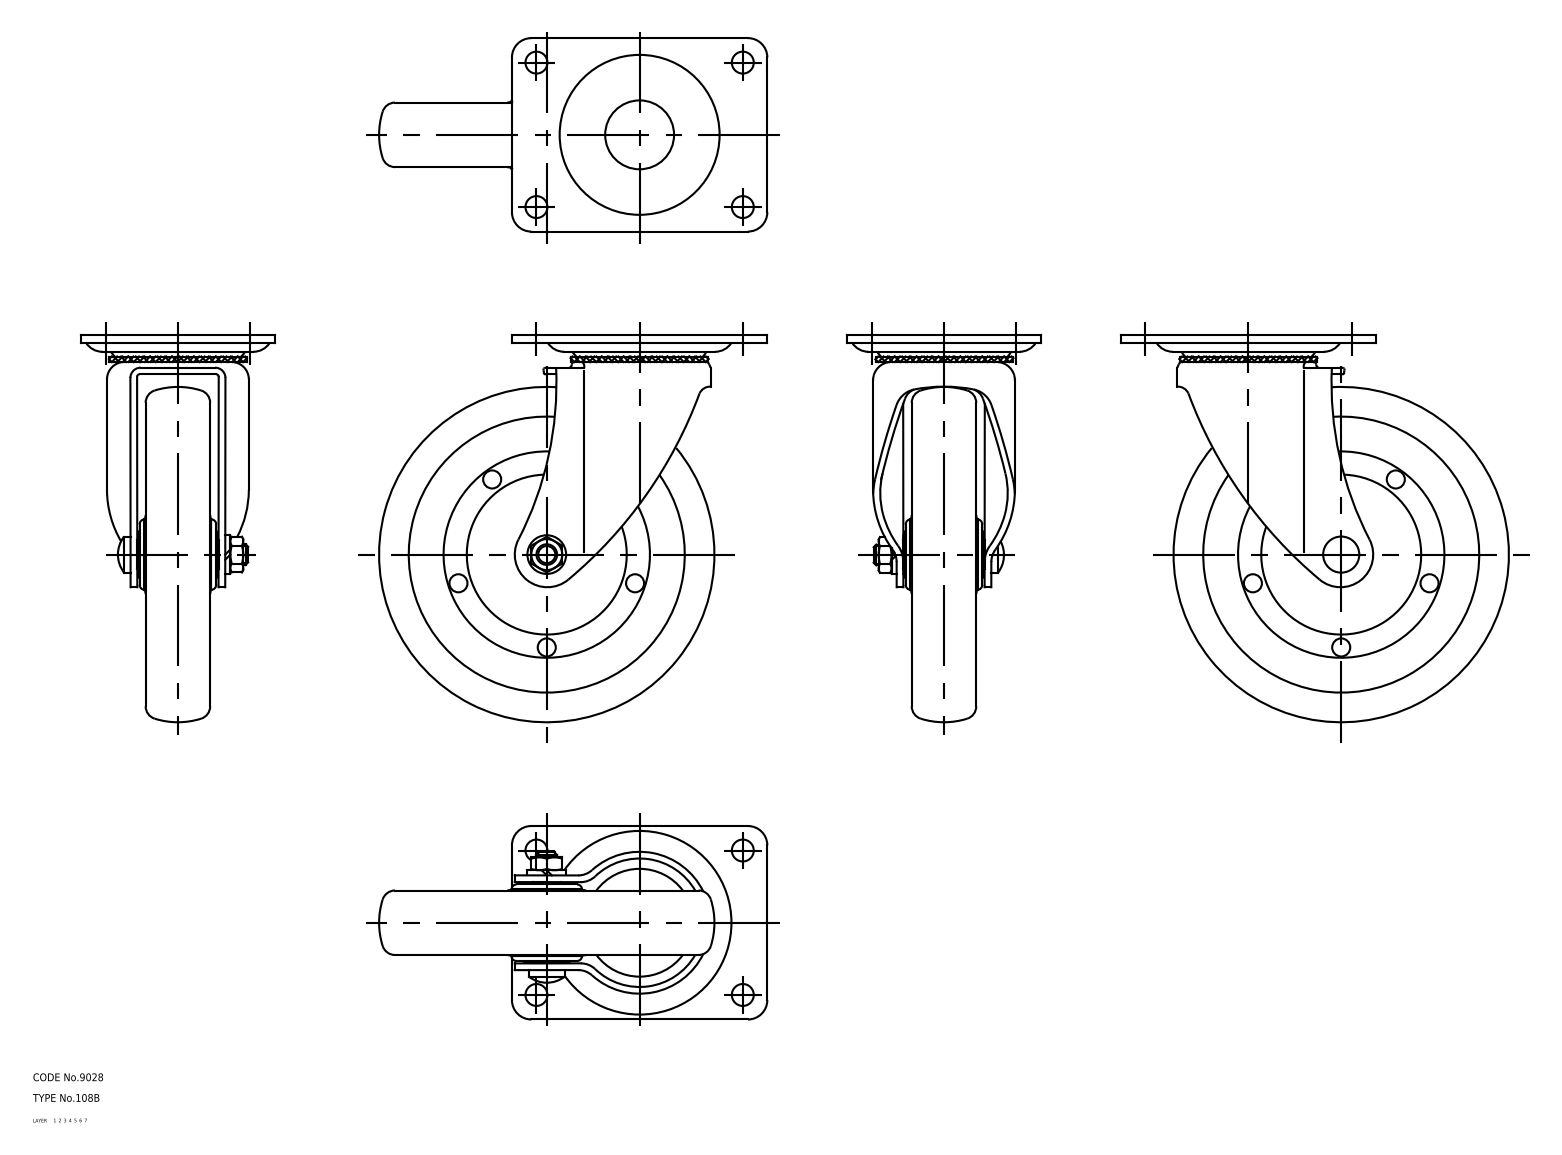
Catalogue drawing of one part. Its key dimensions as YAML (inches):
part_name: "67126640; 67126653; 67126666; 67126679 (+8 more)"
step_written_by: "CADfix (AUTOMOTIVE_DESIGN)"
units: inches
bodies: {solids: 4, faces: 226, planar: 0, cylindrical: 0, other: 226}
overall_size: [5.925, 5.906, 2.953]
volume: 19.22
surface_area: 125.6
